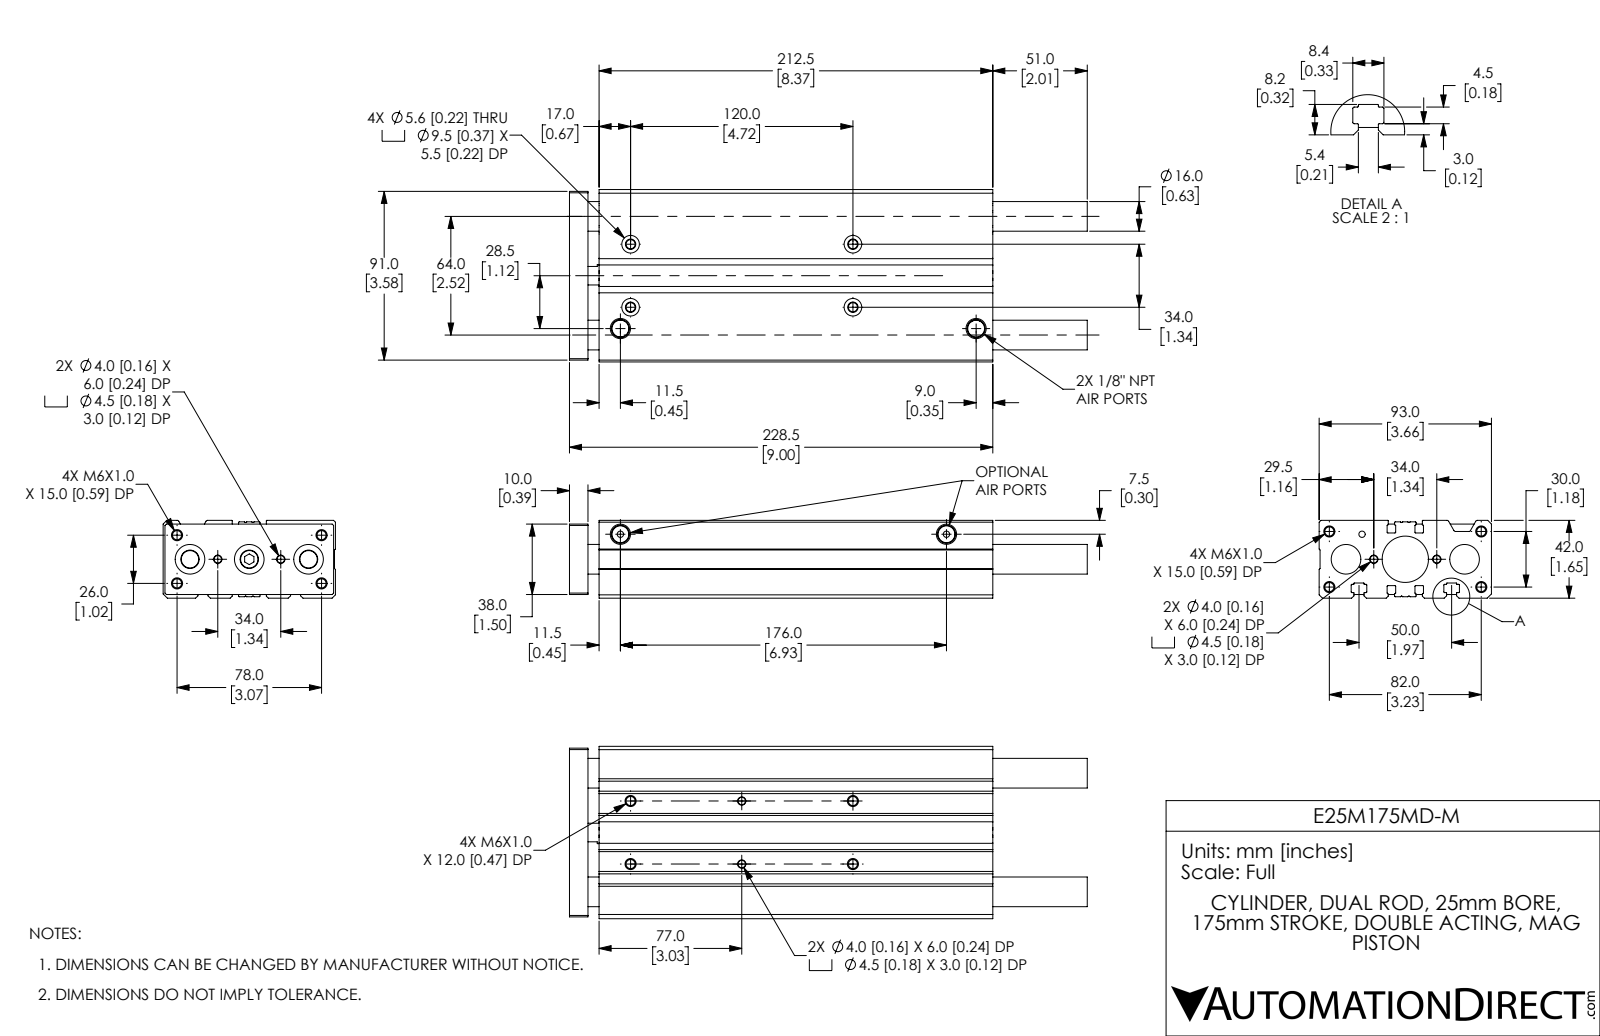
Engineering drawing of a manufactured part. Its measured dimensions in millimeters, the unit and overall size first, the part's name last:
Units: millimetres
Overall size (bounding box): 279.5 × 93 × 42
Round holes (diameter × count): ⌀4.92 ×10, ⌀4 ×4, ⌀4.5 ×4, ⌀5.6 ×4, ⌀9.5 ×4, ⌀8 ×3, ⌀16 ×3, ⌀3.43 ×2, ⌀4.92 ×2, ⌀9.91 ×2, ⌀3.43 ×1, ⌀16 ×1
Round bosses / shafts (diameter × count): ⌀12 ×1, ⌀9.91 ×1
Partial cylindrical surfaces — rounded edges, fillets, slot ends (radius × count): R0.2 ×32, R0.4 ×28, R1 ×4, R0.3 ×2
Main face-to-face distances: 42, 6, 93, 0.8, 34.4, 15, 35.2, 41.2, 6.8, 41.3
Hole centre spacings: 2.83, 14.76, 17.49, 25.55, 28.07, 28.3, 34, 41.11
Volume: 738 030 mm³ · Surface area: 178 641 mm²
Bodies: 5 solids, 423 faces (139 planar, 190 cylindrical, 94 other)
Part name (STEP PRODUCT): E25M175MD-M_BODY; E25M175MD-M_ENDPLATE; E25M175MD-M
STEP written by: SolidWorks 2019 (CONFIG_CONTROL_DESIGN)
